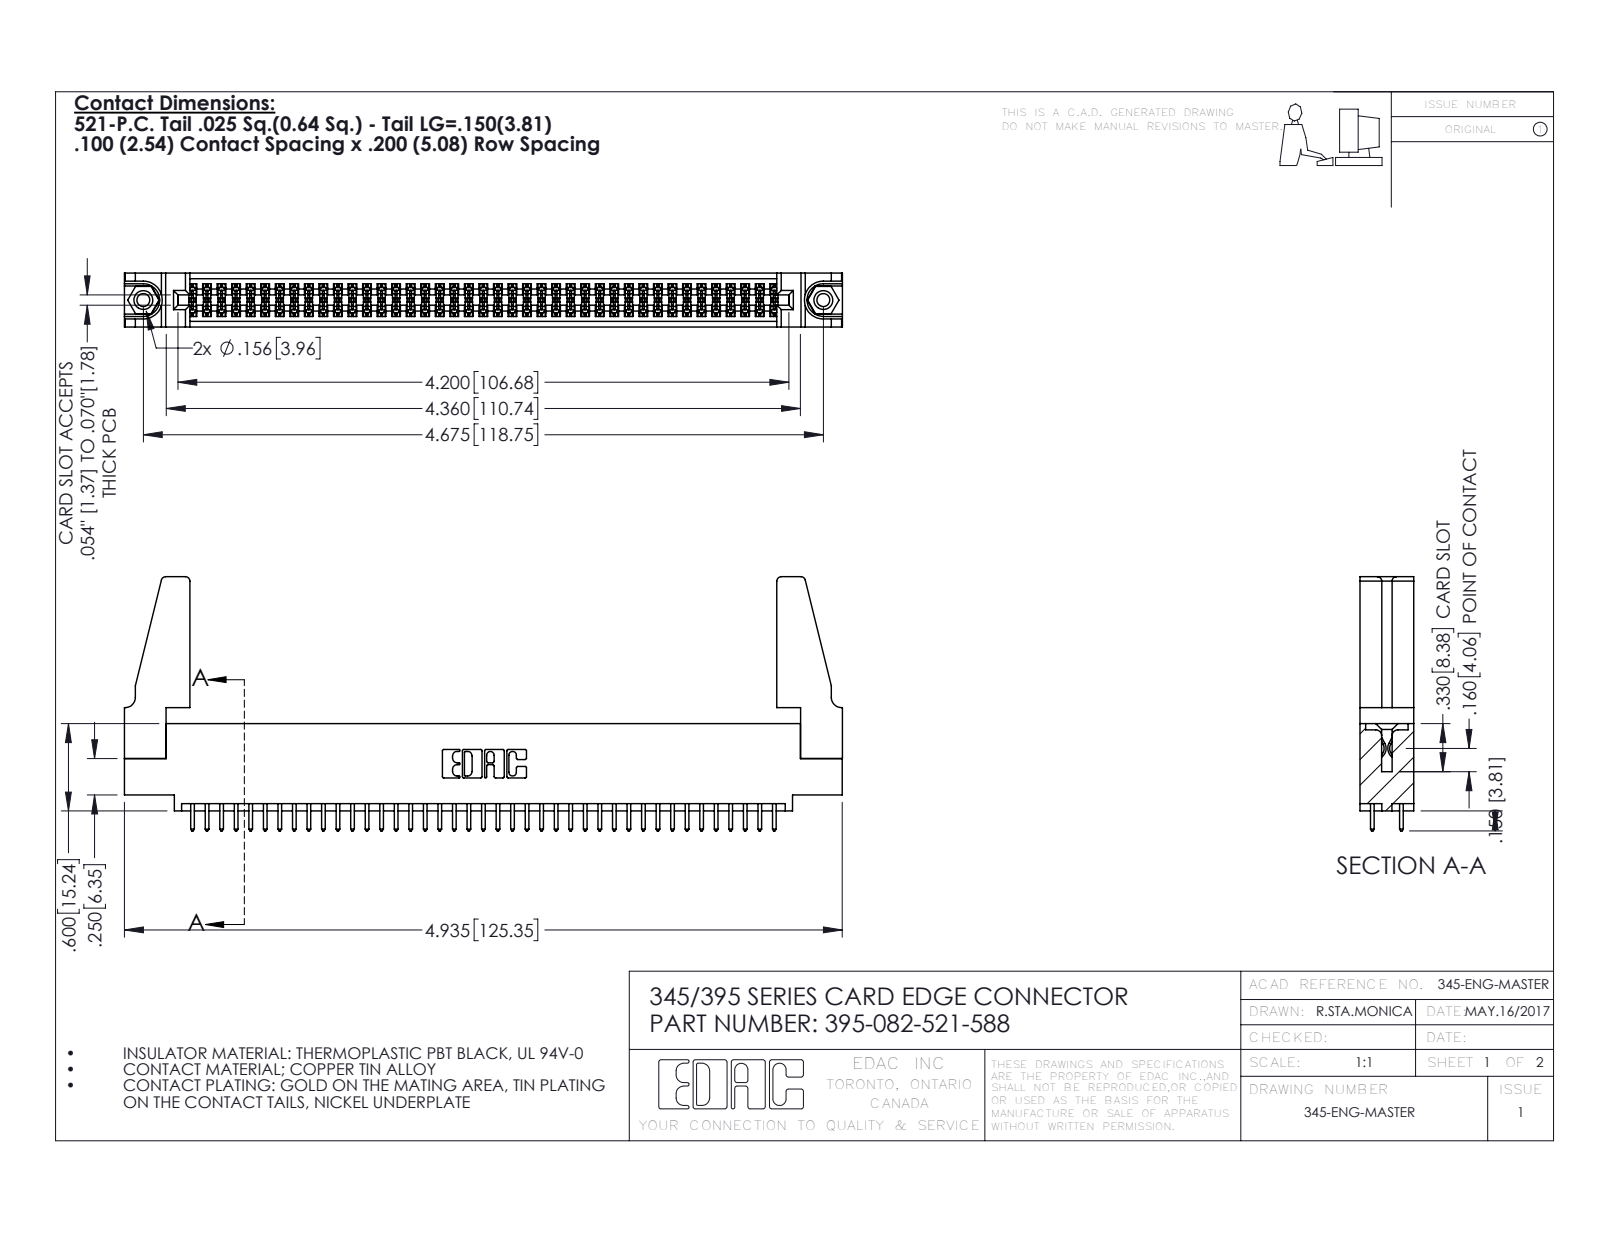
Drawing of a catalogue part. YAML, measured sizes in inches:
part_name: "345-250-001_345-250-001-102; 345-220-078_345-220-088; 345 Part_0.110 Offset - 0.156 Dia-TH; 345-292-001_345-293-121 (+1 more)"
step_written_by: "SolidWorks 2016 (CONFIG_CONTROL_DESIGN)"
units: inches
bodies: {solids: 87, faces: 4354, planar: 2862, cylindrical: 1476, other: 16}
overall_size: [4.936, 1.747, 0.37]
volume: 0.935
surface_area: 32.25
round_holes:
  - {diameter: 0.089, count: 2}
  - {diameter: 0.125, count: 2}
  - {diameter: 0.156, count: 2}
  - {diameter: 0.064, count: 1}
round_bosses_or_shafts:
  - {diameter: 0.155, count: 2}
partial_cylinders:
  - {radius: 0.006, count: 123}
  - {radius: 0.01, count: 82}
  - {radius: 0.01, count: 22}
  - {radius: 0.03, count: 8}
  - {radius: 0.007, count: 6}
  - {radius: 0.031, count: 6}
  - {radius: 0.026, count: 3}
  - {radius: 0.014, count: 2}
face_to_face_distances: [0.072, 0.298, 0.37, 0.2, 0.098, 0.272, 0.025, 0.225, 0.175, 0.149]
hole_center_spacings: [0.27, 4.439, 4.675]
